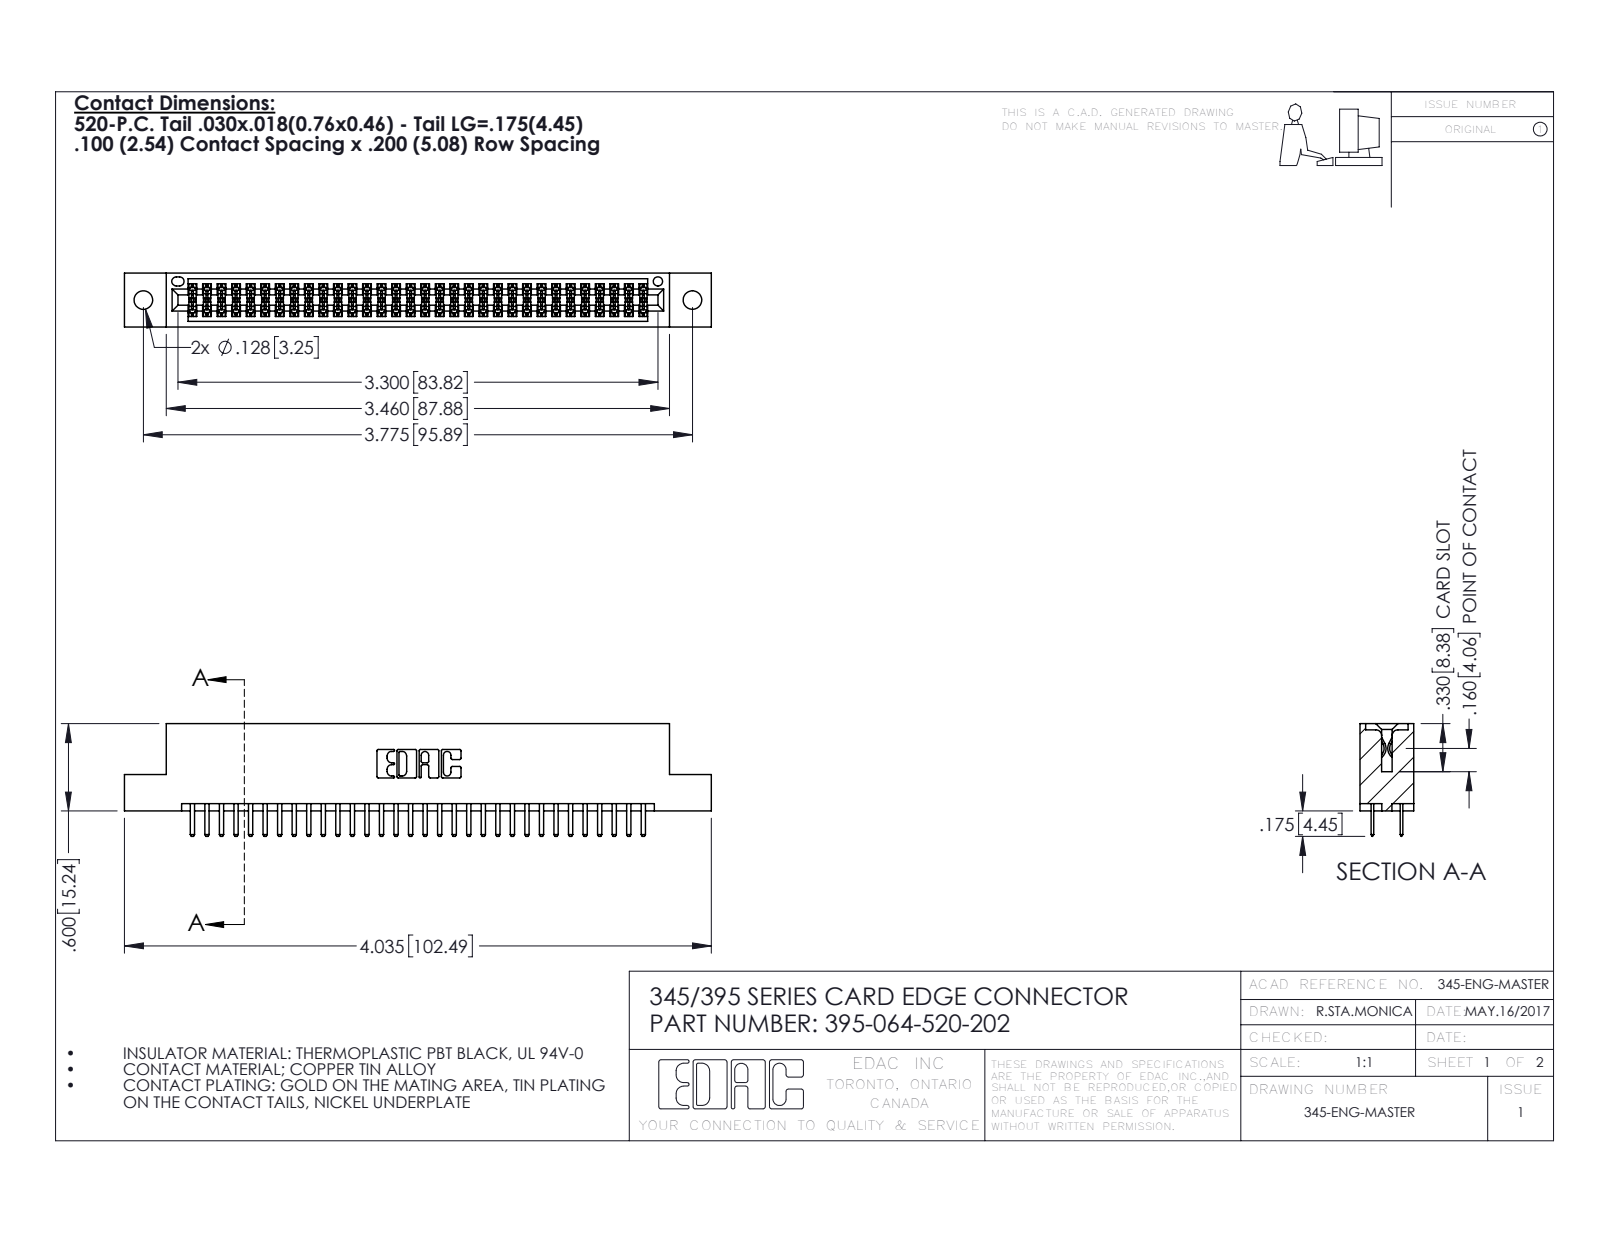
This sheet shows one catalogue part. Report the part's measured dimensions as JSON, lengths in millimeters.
{"part_name": "395-064-520-202; 345-292-001_345-293-120; 345 Part_Flush Mounting Lugs - 0.128 Dia", "step_written_by": "SolidWorks 2016 (CONFIG_CONTROL_DESIGN)", "units": "millimeters", "bodies": {"solids": 65, "faces": 3582, "planar": 2320, "cylindrical": 1262, "other": 0}, "overall_size": [102.5, 19.7, 9.4], "volume_mm3": 9800, "surface_area_mm2": 13950, "round_holes": [[3.3, 2], [1.6, 1]], "partial_cylinders_radius": [[0.2, 96], [0.3, 68], [0.3, 22], [0.2, 6], [0.8, 6], [0.7, 3], [0.4, 2], [0.5, 2]], "face_to_face_distances": [7.6, 1.8, 5.1, 9.4, 2.5, 6.9, 0.6, 5.7, 0.6, 1.8], "hole_center_spacings": [6.9, 89.9, 95.9]}
